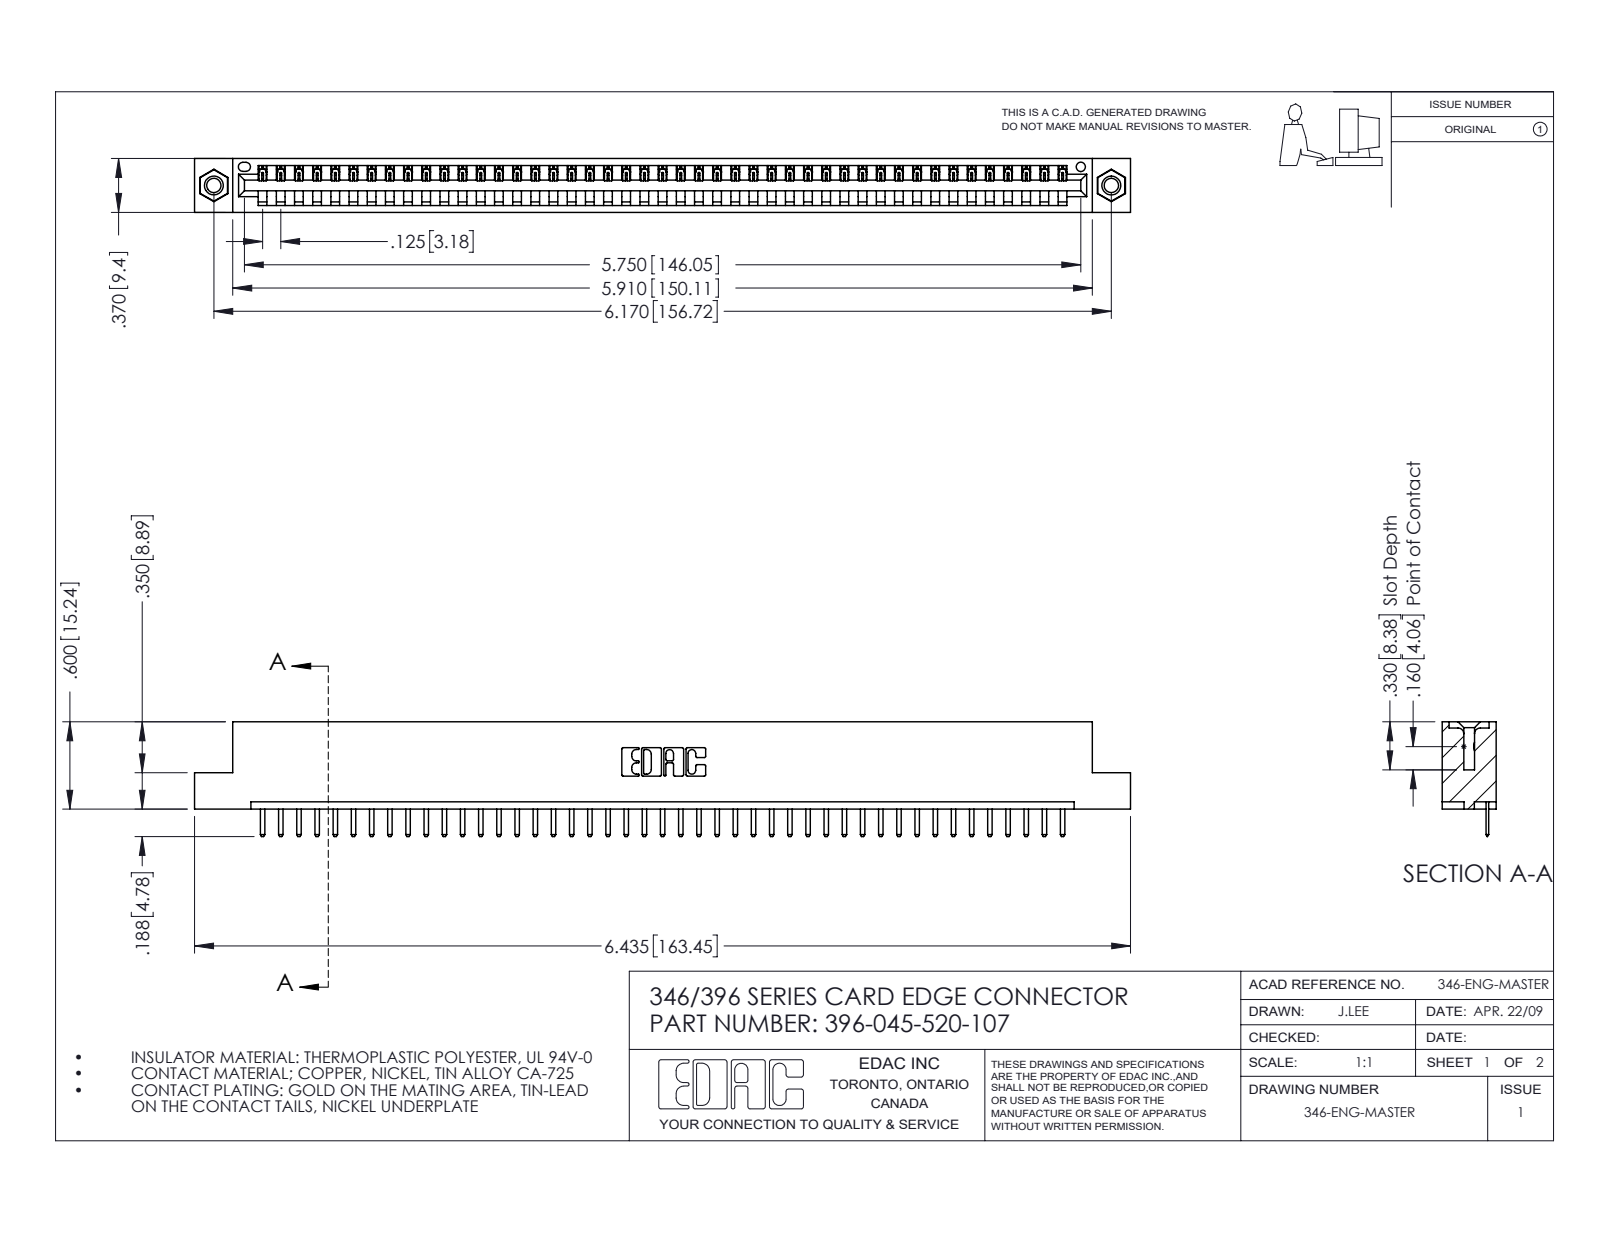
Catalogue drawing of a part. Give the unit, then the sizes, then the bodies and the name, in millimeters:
Units: millimetres
Overall size (bounding box): 163.4 × 20 × 9.4
Round holes (diameter × count): ⌀2.5 ×2, ⌀3.2 ×2, ⌀4 ×2, ⌀1.6 ×1
Round bosses / shafts (diameter × count): ⌀3.9 ×2
Partial cylindrical surfaces — rounded edges, fillets, slot ends (radius × count): R0.3 ×92, R0.2 ×90, R0.3 ×22, R0.2 ×6, R0.8 ×6, R0.7 ×3, R0.8 ×2, R1 ×2
Main face-to-face distances: 1.2, 8.2, 9.4, 6.4, 3.8, 5.6, 2.5, 4.4, 1.8, 7.6
Hole centre spacings: 6.2, 151.4, 156.7
Volume: 15 500 mm³ · Surface area: 19 040 mm²
Bodies: 48 solids, 2972 faces (1998 planar, 958 cylindrical, 16 other)
Part name (STEP PRODUCT): 345-250-001_345-250-005-103; 396-045-520-107; 345-292-001_345-293-120; 346 Part_Flush Mounting Lugs - 0.156 Dia-TI
STEP written by: SolidWorks 2016 (CONFIG_CONTROL_DESIGN)
